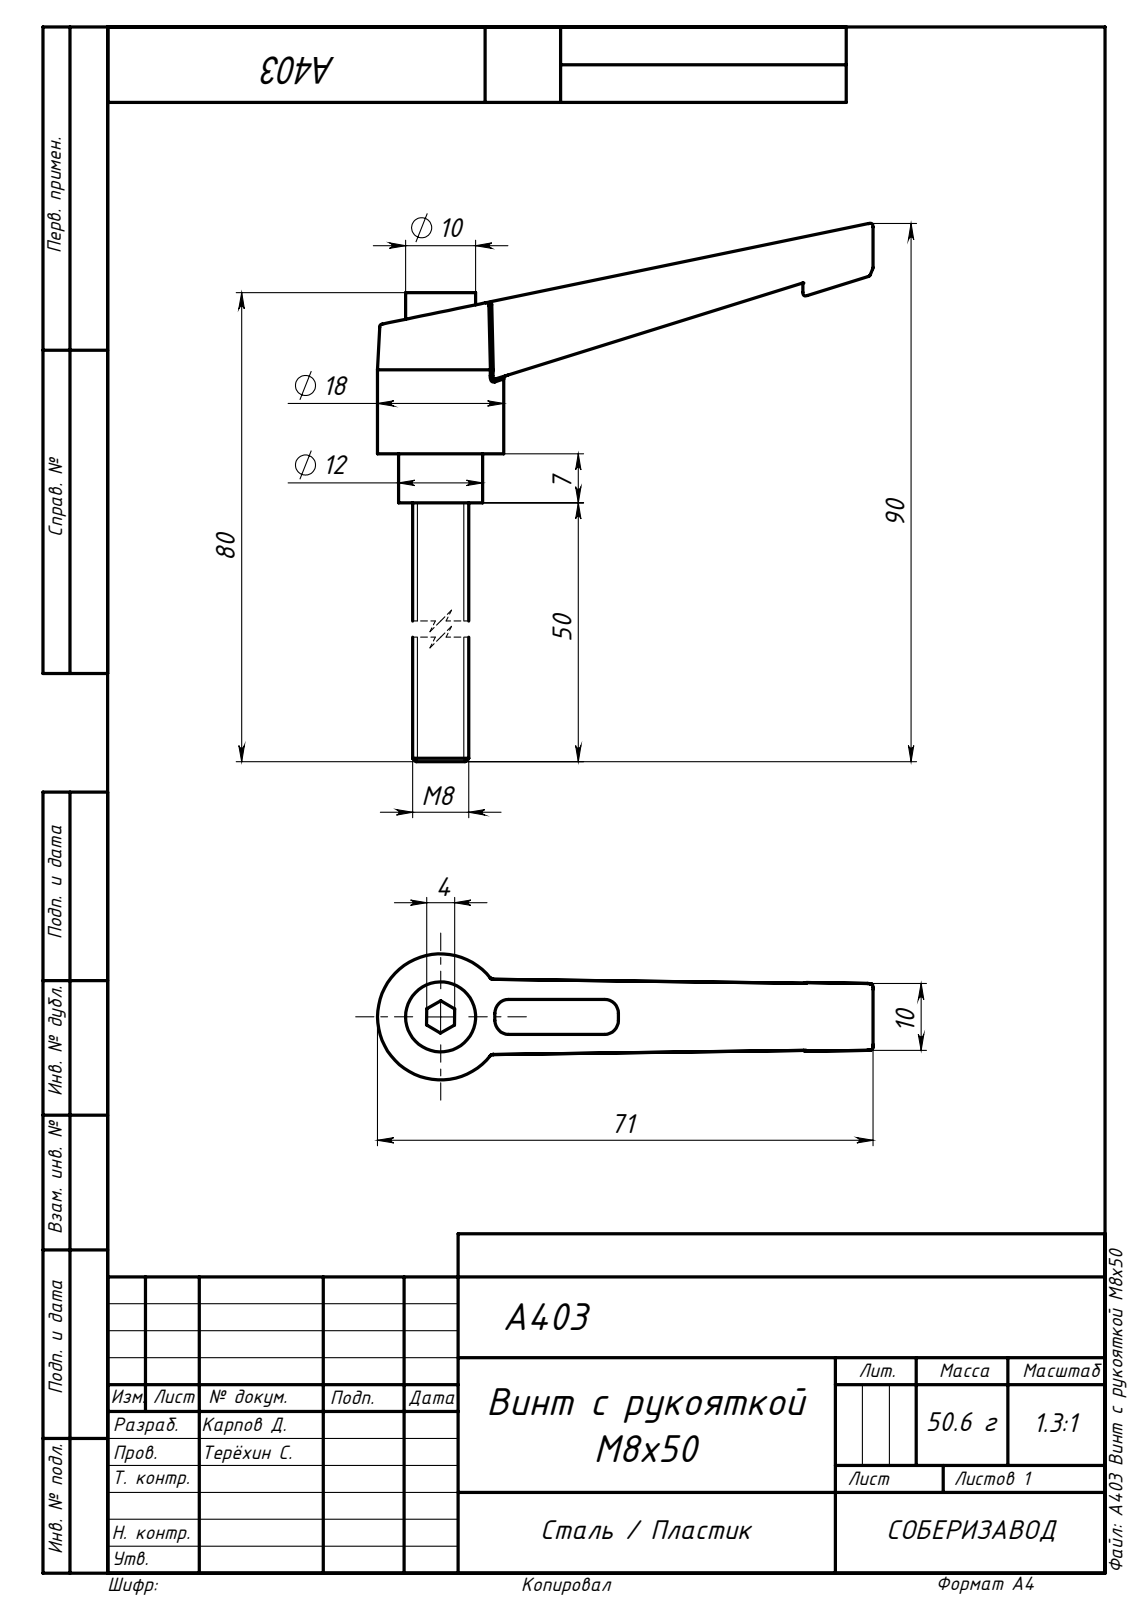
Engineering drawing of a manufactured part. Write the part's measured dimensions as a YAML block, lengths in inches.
part_name: "A403 Винт с рукояткой М8х50"
step_written_by: "SolidWorks 2020 (AUTOMOTIVE_DESIGN)"
units: inches
bodies: {solids: 1, faces: 79, planar: 29, cylindrical: 12, other: 38}
overall_size: [3.539, 2.783, 0.709]
volume: 0.67
surface_area: 8.902
round_bosses_or_shafts:
  - {diameter: 0.709, count: 1}
  - {diameter: 0.472, count: 1}
  - {diameter: 0.394, count: 1}
  - {diameter: 0.315, count: 1}
partial_cylinders:
  - {radius: 0.079, count: 4}
face_to_face_distances: [0.272, 0.906, 0.276, 1.181, 1.737, 1.969, 2.244, 3.15, 0.157, 3.031]
